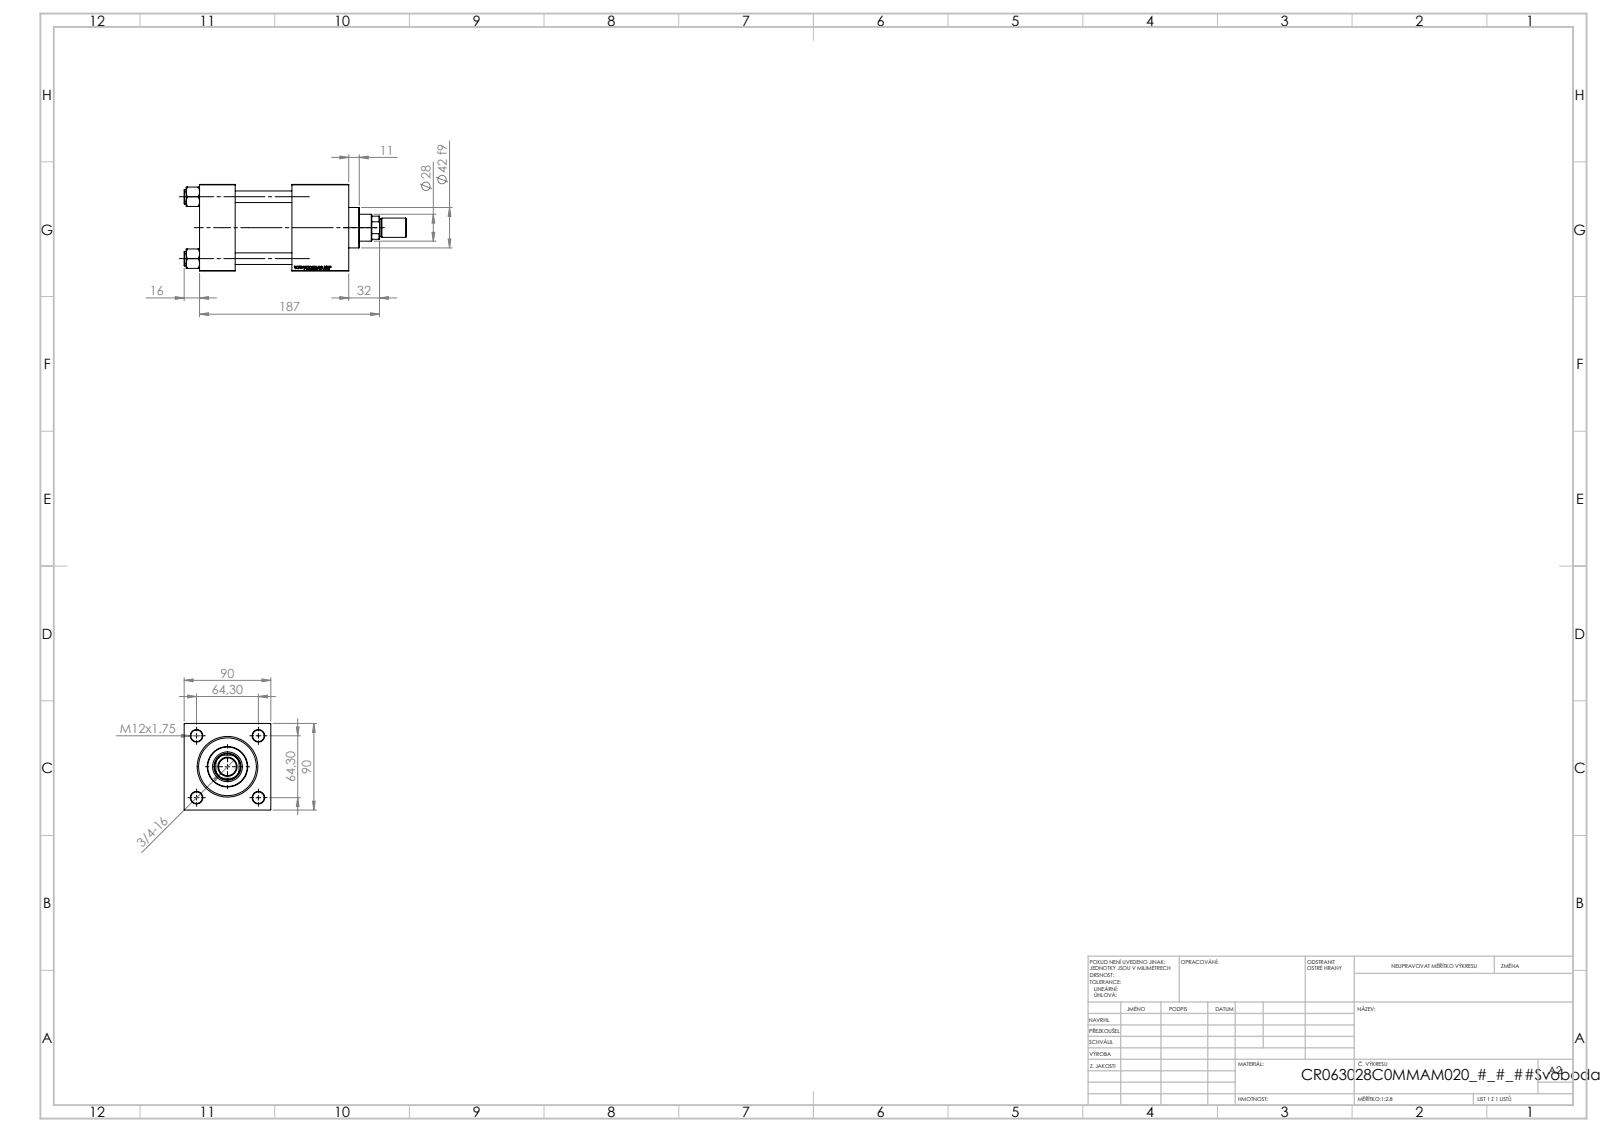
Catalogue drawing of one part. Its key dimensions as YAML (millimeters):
part_name: "NUT_M5_C; V215CR_VCP_C; ROD_END_AH; V215_VC_A (+2 more)"
step_written_by: "SolidWorks 2019 (CONFIG_CONTROL_DESIGN)"
units: millimeters
bodies: {solids: 12, faces: 1162, planar: 530, cylindrical: 90, other: 542}
overall_size: [231, 90, 90]
volume: 955910
surface_area: 181452
round_holes:
  - {diameter: 12, count: 4}
  - {diameter: 7, count: 2}
  - {diameter: 20.96, count: 2}
  - {diameter: 30, count: 2}
  - {diameter: 18.5, count: 1}
  - {diameter: 28, count: 1}
  - {diameter: 31, count: 1}
  - {diameter: 50, count: 1}
  - {diameter: 60, count: 1}
  - {diameter: 63, count: 1}
round_bosses_or_shafts:
  - {diameter: 15, count: 4}
  - {diameter: 69, count: 1}
  - {diameter: 42, count: 1}
  - {diameter: 20, count: 1}
  - {diameter: 18, count: 1}
partial_cylinders:
  - {radius: 13.5, count: 1}
face_to_face_distances: [90, 59, 37, 155, 118, 96, 126.3, 89.3, 30.3, 28.7]
hole_center_spacings: [45.47, 64.3, 90.93, 97.5]
